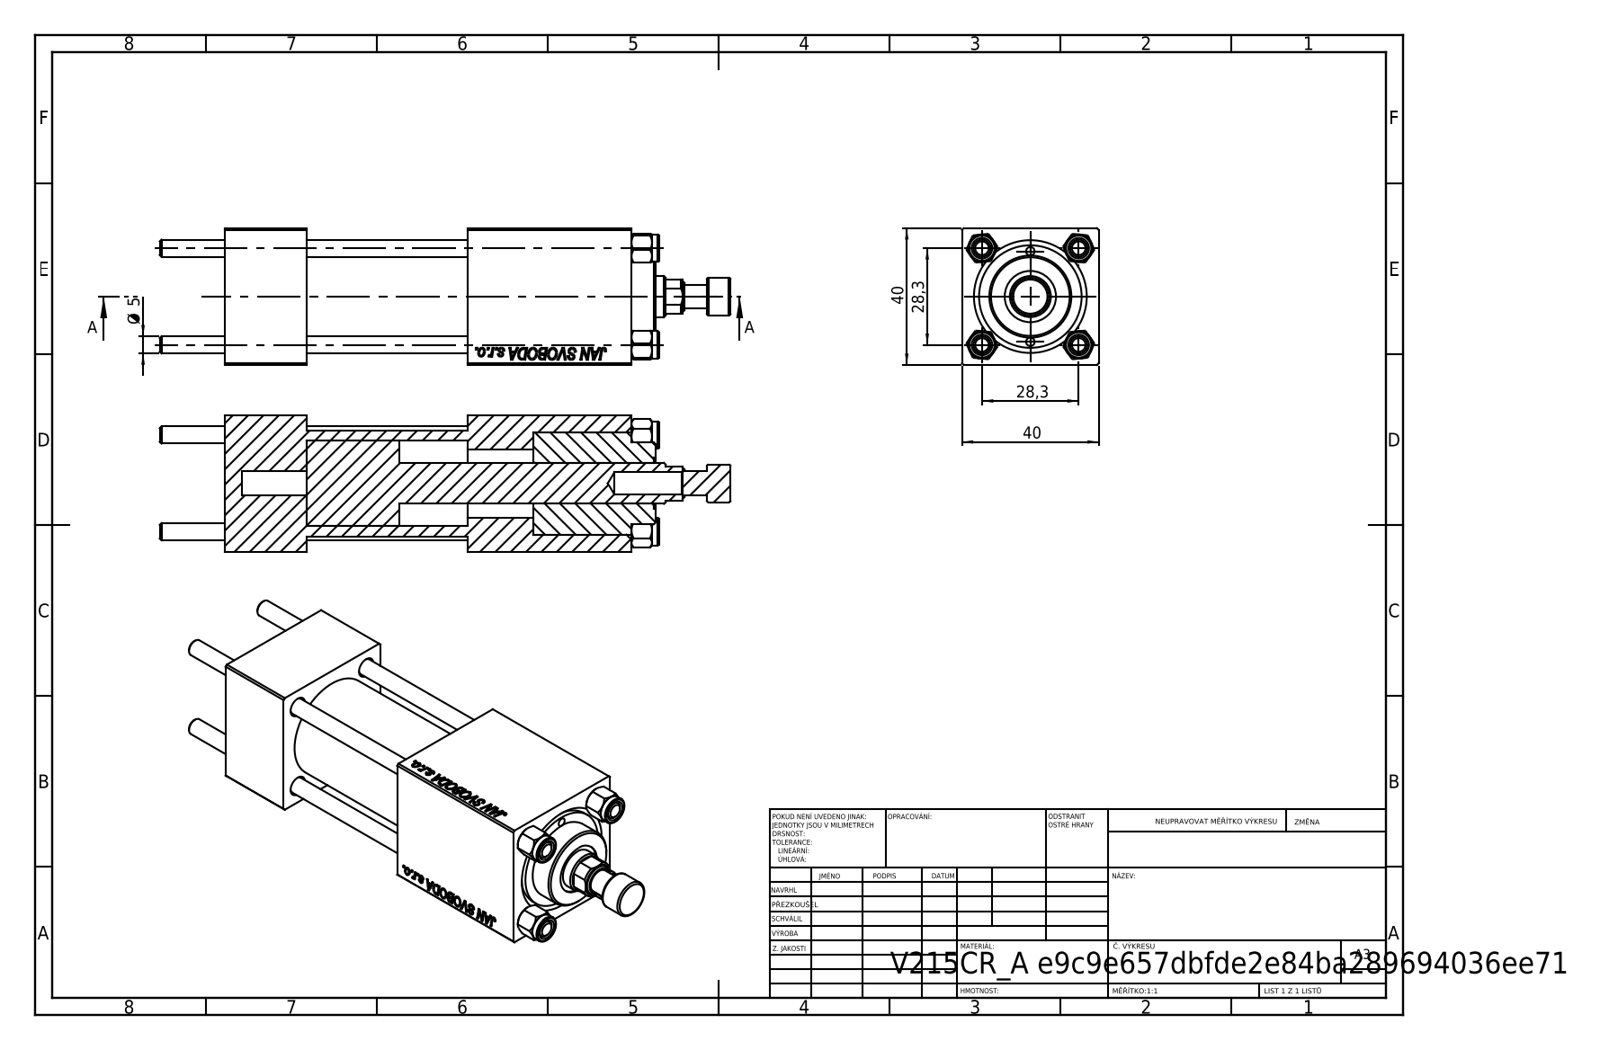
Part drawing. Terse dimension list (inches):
name: CR025_012_A_0_G_A_G_M_020_+#_##_TYCINKA; V215CR_ROD_END_F; V215CR_BODY_A; NUT_M5 (+2 more)
written by: SolidWorks 2019 (CONFIG_CONTROL_DESIGN)
unit: in
bodies: 12 solids, 1151 faces (523 planar, 86 cylindrical, 542 other)
size: 6.575 × 1.575 × 1.575
volume: 8.892 in³; area: 92.33 in²
holes: 4× ⌀0.197, 3× ⌀0.787, 2× ⌀0.098, 2× ⌀0.276, 2× ⌀0.518, 1× ⌀0.256, 1× ⌀0.472, 1× ⌀0.591, 1× ⌀0.984, 1× ⌀1.181
bosses: 4× ⌀0.315, 1× ⌀1.22, 1× ⌀0.945, 1× ⌀0.433
face distances: 1.575, 0.945, 3.555, 2.61, 4.685, 3.74, 1.13, 2.795, 1.85, 0.76
hole spacings: 0.558, 0.788, 1.114, 1.214, 0.522, 1.576, 1.043, 2.835
